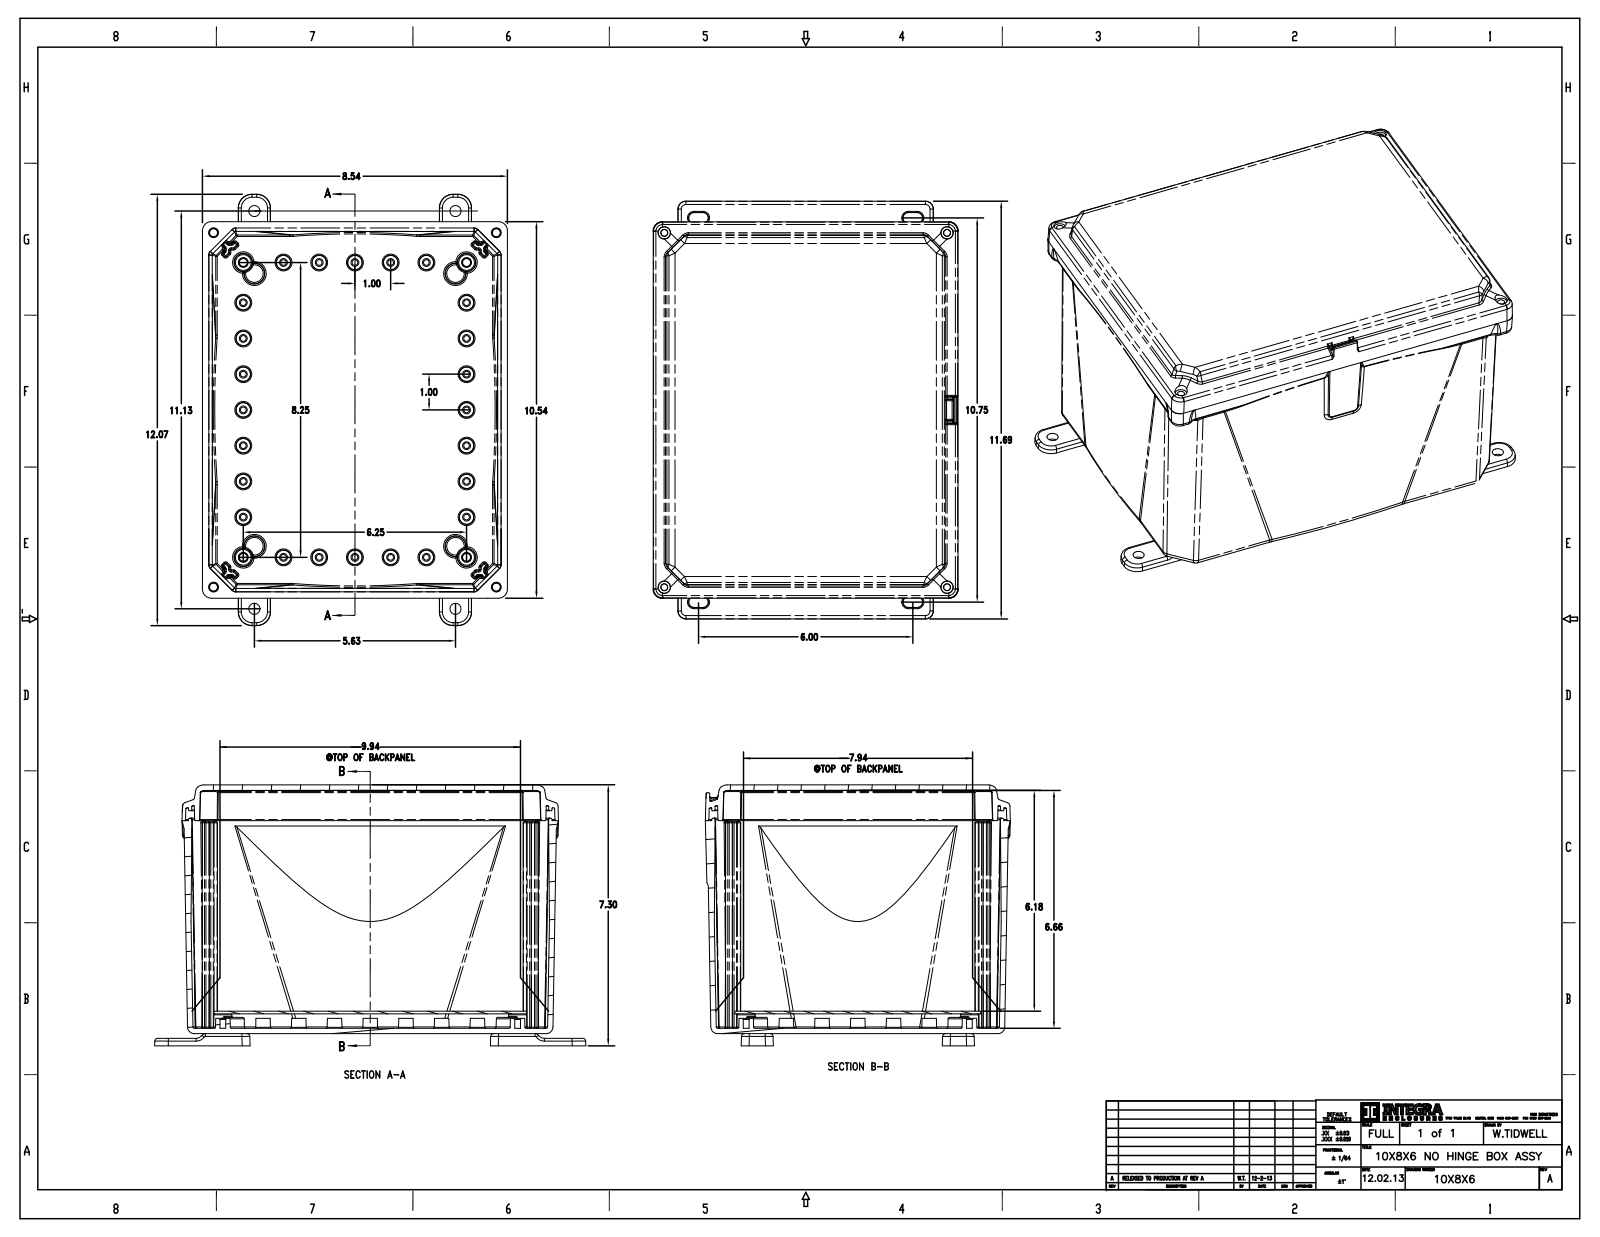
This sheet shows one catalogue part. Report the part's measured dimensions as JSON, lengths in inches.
{"part_name": "1008600; 1008640; 1008690; 8INCH-MOUNTING-FLANGE (+1 more)", "step_written_by": "CREO PARAMETRIC BY PTC INC, 2016050 (CONFIG_CONTROL_DESIGN)", "units": "inches", "bodies": {"solids": 5, "faces": 2874, "planar": 598, "cylindrical": 1088, "other": 1188}, "overall_size": [11.69, 8.536, 7.303], "volume_in3": 77.79, "surface_area_in2": 1119, "round_holes": [[0.16, 24], [0.25, 4]], "partial_cylinders_radius": [[0.03, 339], [0.02, 166], [0.09, 38], [0.04, 36], [0.08, 26], [0.06, 21], [0.2, 20], [0.025, 16]], "face_to_face_distances": [0.15, 0.555, 0.405, 0.618, 0.468, 0.063, 0.49, 5.81, 0.12, 5.96], "hole_center_spacings": [1, 2, 3, 6.33, 6.563, 6.25, 2.404, 3.321]}
